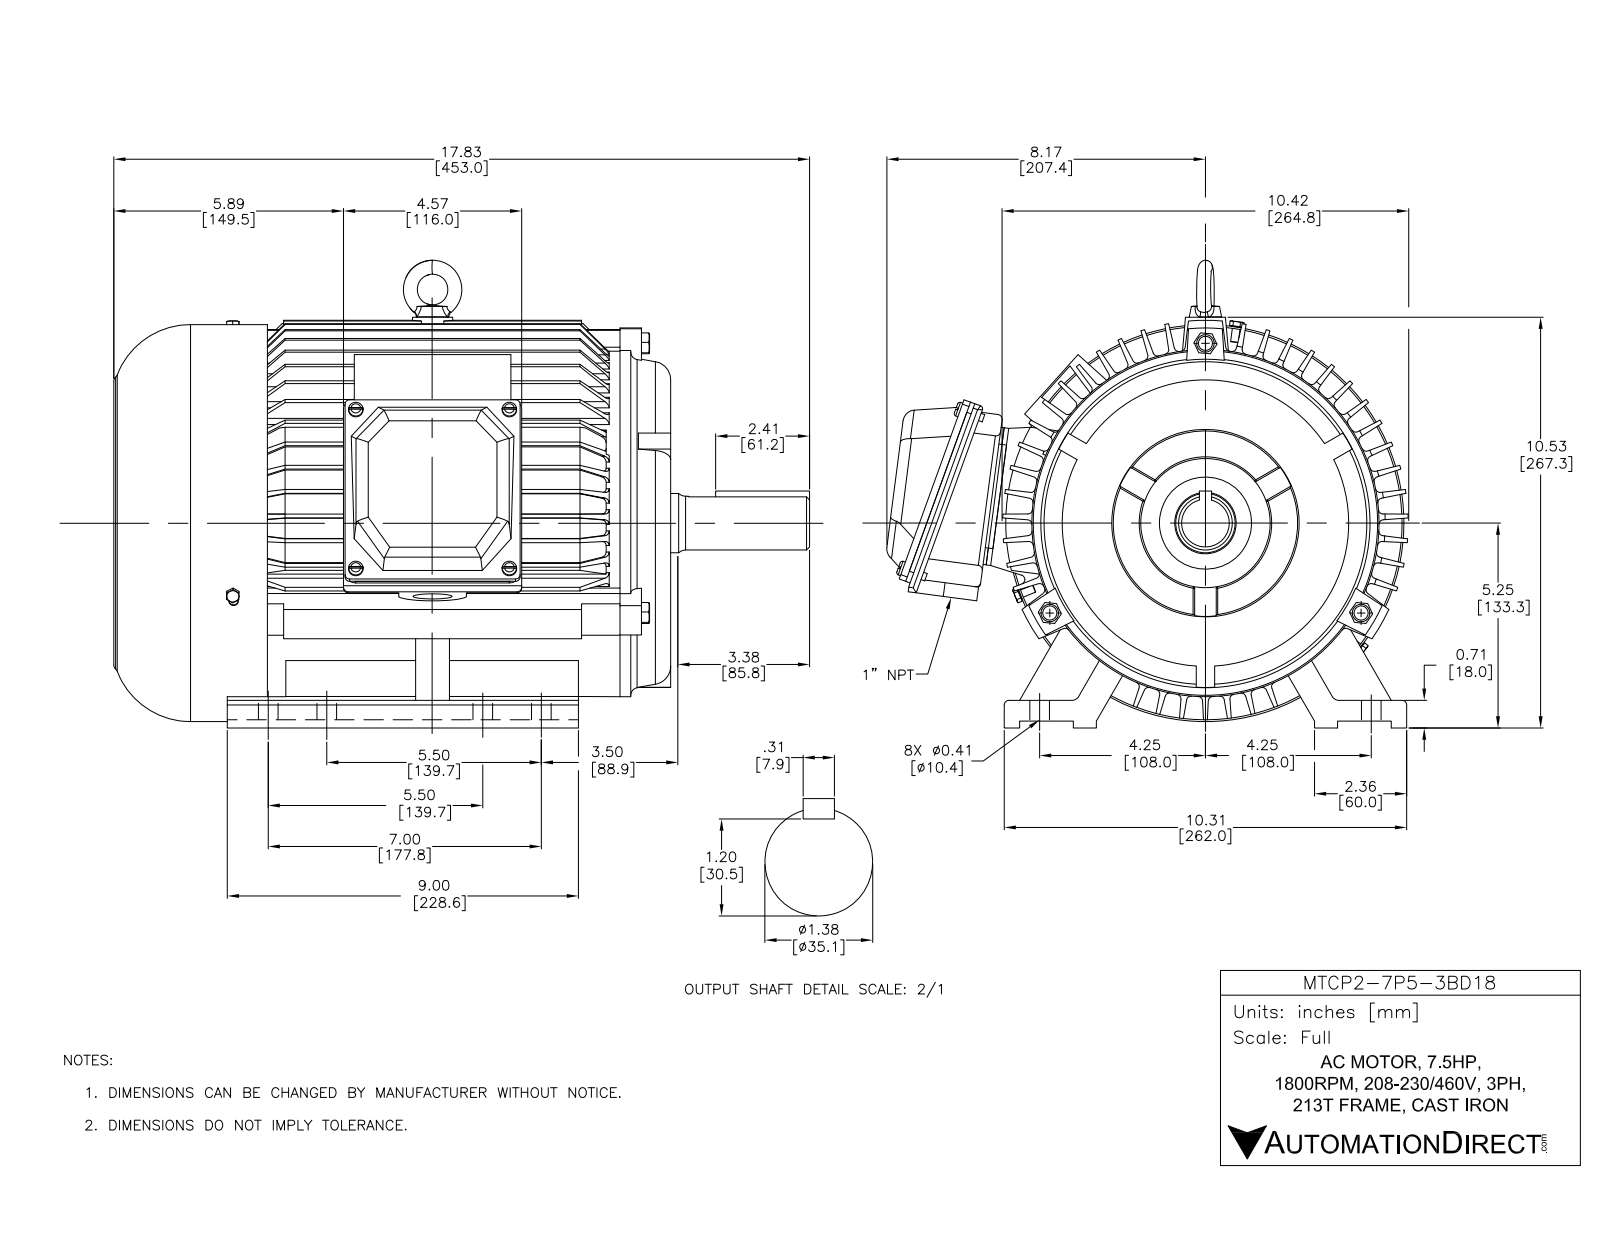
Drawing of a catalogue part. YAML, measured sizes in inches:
part_name: "MTCP2-7P5-3BD18"
step_written_by: "SolidWorks 2017 (AUTOMOTIVE_DESIGN)"
units: inches
bodies: {solids: 19, faces: 1770, planar: 1030, cylindrical: 476, other: 264}
overall_size: [17.835, 13.363, 11.986]
volume: 235.3
surface_area: 1916
round_holes:
  - {diameter: 0.228, count: 8}
  - {diameter: 0.433, count: 8}
  - {diameter: 0.197, count: 6}
  - {diameter: 0.165, count: 4}
  - {diameter: 0.236, count: 4}
  - {diameter: 0.276, count: 4}
  - {diameter: 0.315, count: 3}
  - {diameter: 0.362, count: 3}
  - {diameter: 0.394, count: 3}
  - {diameter: 0.335, count: 1}
  - {diameter: 0.453, count: 1}
  - {diameter: 1, count: 1}
round_bosses_or_shafts:
  - {diameter: 0.197, count: 7}
  - {diameter: 0.283, count: 3}
  - {diameter: 10.173, count: 1}
  - {diameter: 10.079, count: 1}
  - {diameter: 8.898, count: 1}
  - {diameter: 5.118, count: 1}
  - {diameter: 4.173, count: 1}
  - {diameter: 3.317, count: 1}
partial_cylinders:
  - {radius: 0.118, count: 104}
  - {radius: 0.276, count: 17}
  - {radius: 0.039, count: 12}
  - {radius: 0.059, count: 8}
  - {radius: 0.157, count: 8}
  - {radius: 0.315, count: 8}
  - {radius: 0.091, count: 6}
  - {radius: 0.433, count: 6}
face_to_face_distances: [0.709, 0.157, 14.167, 0.047, 14.215, 0.177, 0.531, 0.236, 13.931, 13.978]
hole_center_spacings: [3.937, 2.677, 4.331, 5.853, 2.678, 3.786, 4.331, 5.853]
